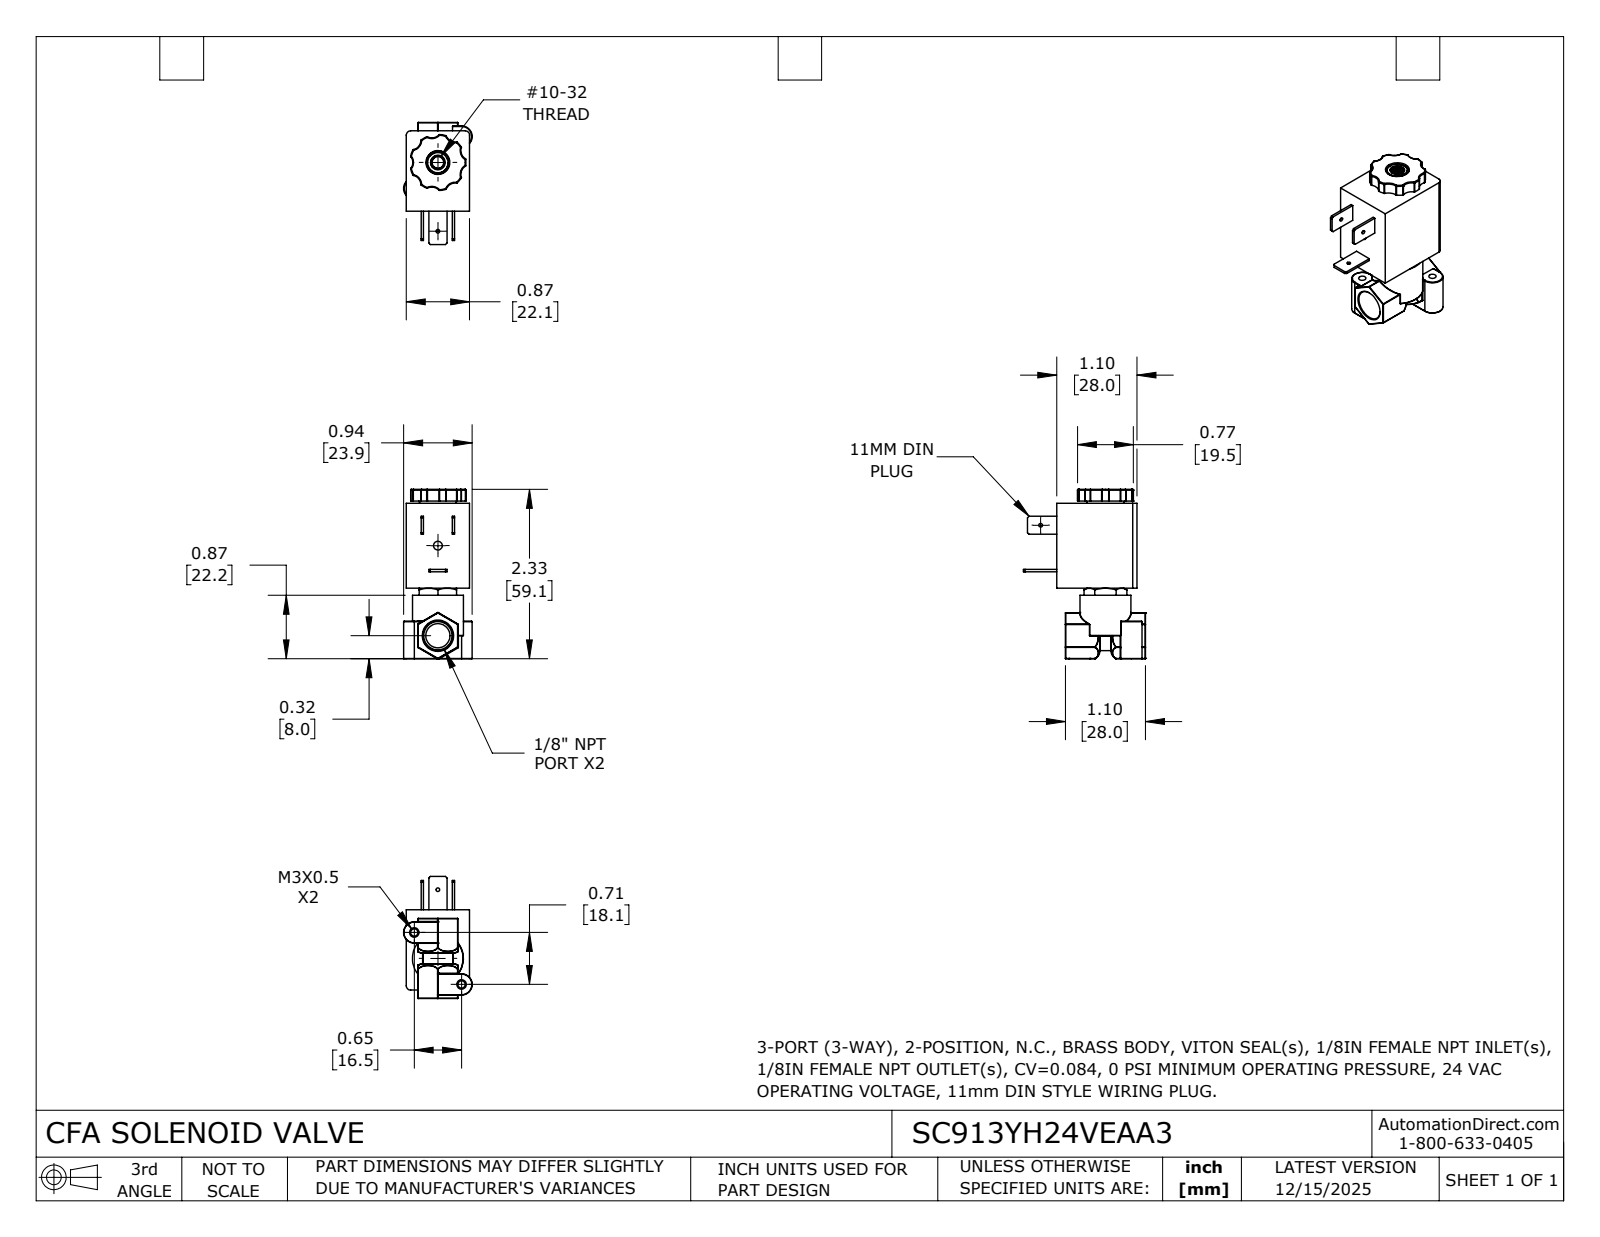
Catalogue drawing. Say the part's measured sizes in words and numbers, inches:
The part is named "SC913YH24VEAA3". Its 3-D file was written by "SolidWorks 2024 (CONFIG_CONTROL_DESIGN)". It is 1 solid with 363 faces: 70 planar, 142 cylindrical and 151 other. Overall it measures 2.328 by 1.678 by 0.942 inches. Its volume is 1.573 cubic inches and its surface area 13.88 square inches. Round holes: 2 of diameter 0.05, 2 of diameter 0.1, 1 of diameter 0.12, 1 of diameter 0.16, 1 of diameter 0.327, 1 of diameter 0.332. Round bosses or shafts: 1 of diameter 0.7, 1 of diameter 0.315. Partial cylindrical surfaces (rounded edges, fillets, slot ends): 29 of radius 0.004, 18 of radius 0.01, 12 of radius 0.008, 7 of radius 0.133, 2 of radius 0.017, 2 of radius 0.06, 2 of radius 0.132, 2 of radius 0.146. The main face-to-face distances are 0.87, 1.104, 1.167, 0.548, 1.357, 0.19, 0.161, 0.709, 0.971, 2.138. The hole center spacings are 0.483, 0.672, 0.945, 0.965, 1.238, 1.342.
